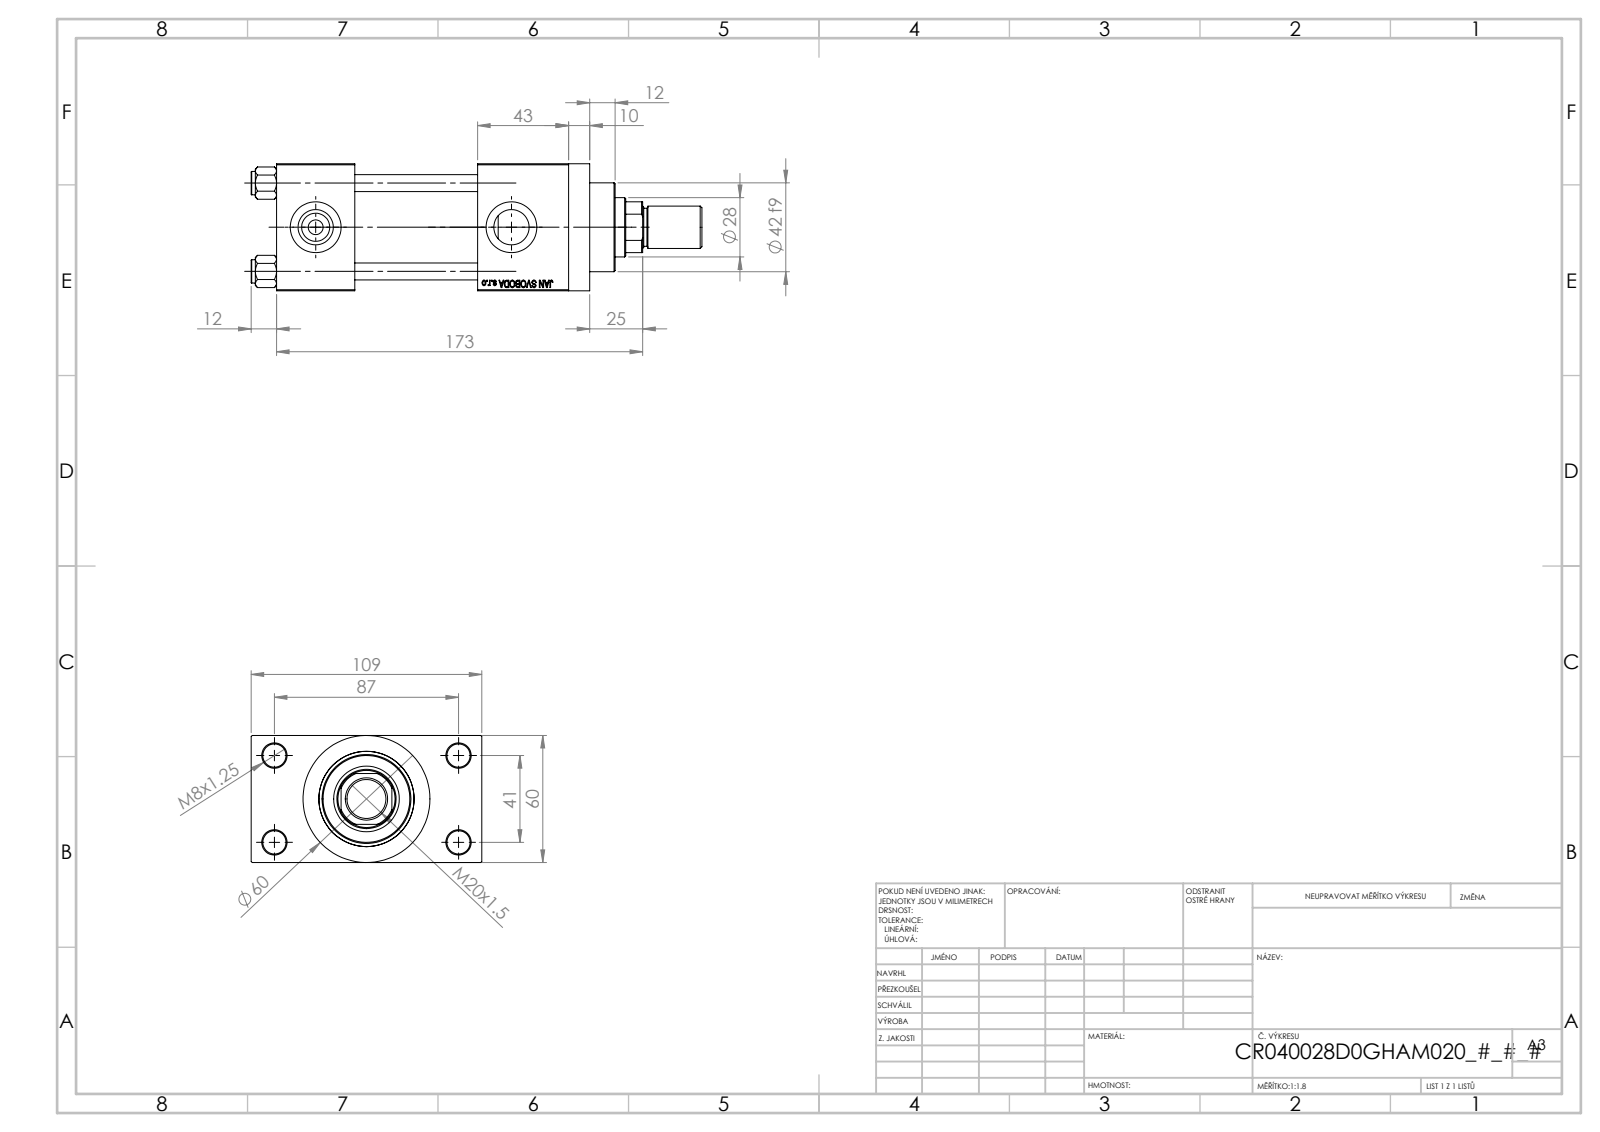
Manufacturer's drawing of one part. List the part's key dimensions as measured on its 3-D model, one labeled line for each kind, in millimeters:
Part name (STEP PRODUCT): ROD_END_AH; V215_VC_A; V215CR_D_Body; NUT_M5_D (+2 more)
STEP written by: SolidWorks 2019 (CONFIG_CONTROL_DESIGN)
Units: millimetres
Bodies: 12 solids, 1118 faces (502 planar, 92 cylindrical, 524 other)
Overall size (bounding box): 213 × 109 × 60
Volume: 537 529 mm³ · Surface area: 131 540 mm²
Round holes (diameter × count): ⌀8 ×4, ⌀11 ×4, ⌀7 ×2, ⌀16.66 ×2, ⌀24 ×2, ⌀18.5 ×1, ⌀28 ×1, ⌀31 ×1, ⌀40 ×1, ⌀45 ×1
Round bosses / shafts (diameter × count): ⌀11 ×4, ⌀60 ×1, ⌀46 ×1, ⌀42 ×1, ⌀20 ×1, ⌀18 ×1
Partial cylindrical surfaces — rounded edges, fillets, slot ends (radius × count): R13.5 ×1
Main face-to-face distances: 60, 58, 24.5, 84.5, 37, 95, 138, 101, 43, 109
Hole centre spacings: 22.65, 29.49, 41.7, 47.15, 48.09, 64.35, 76.49, 41
